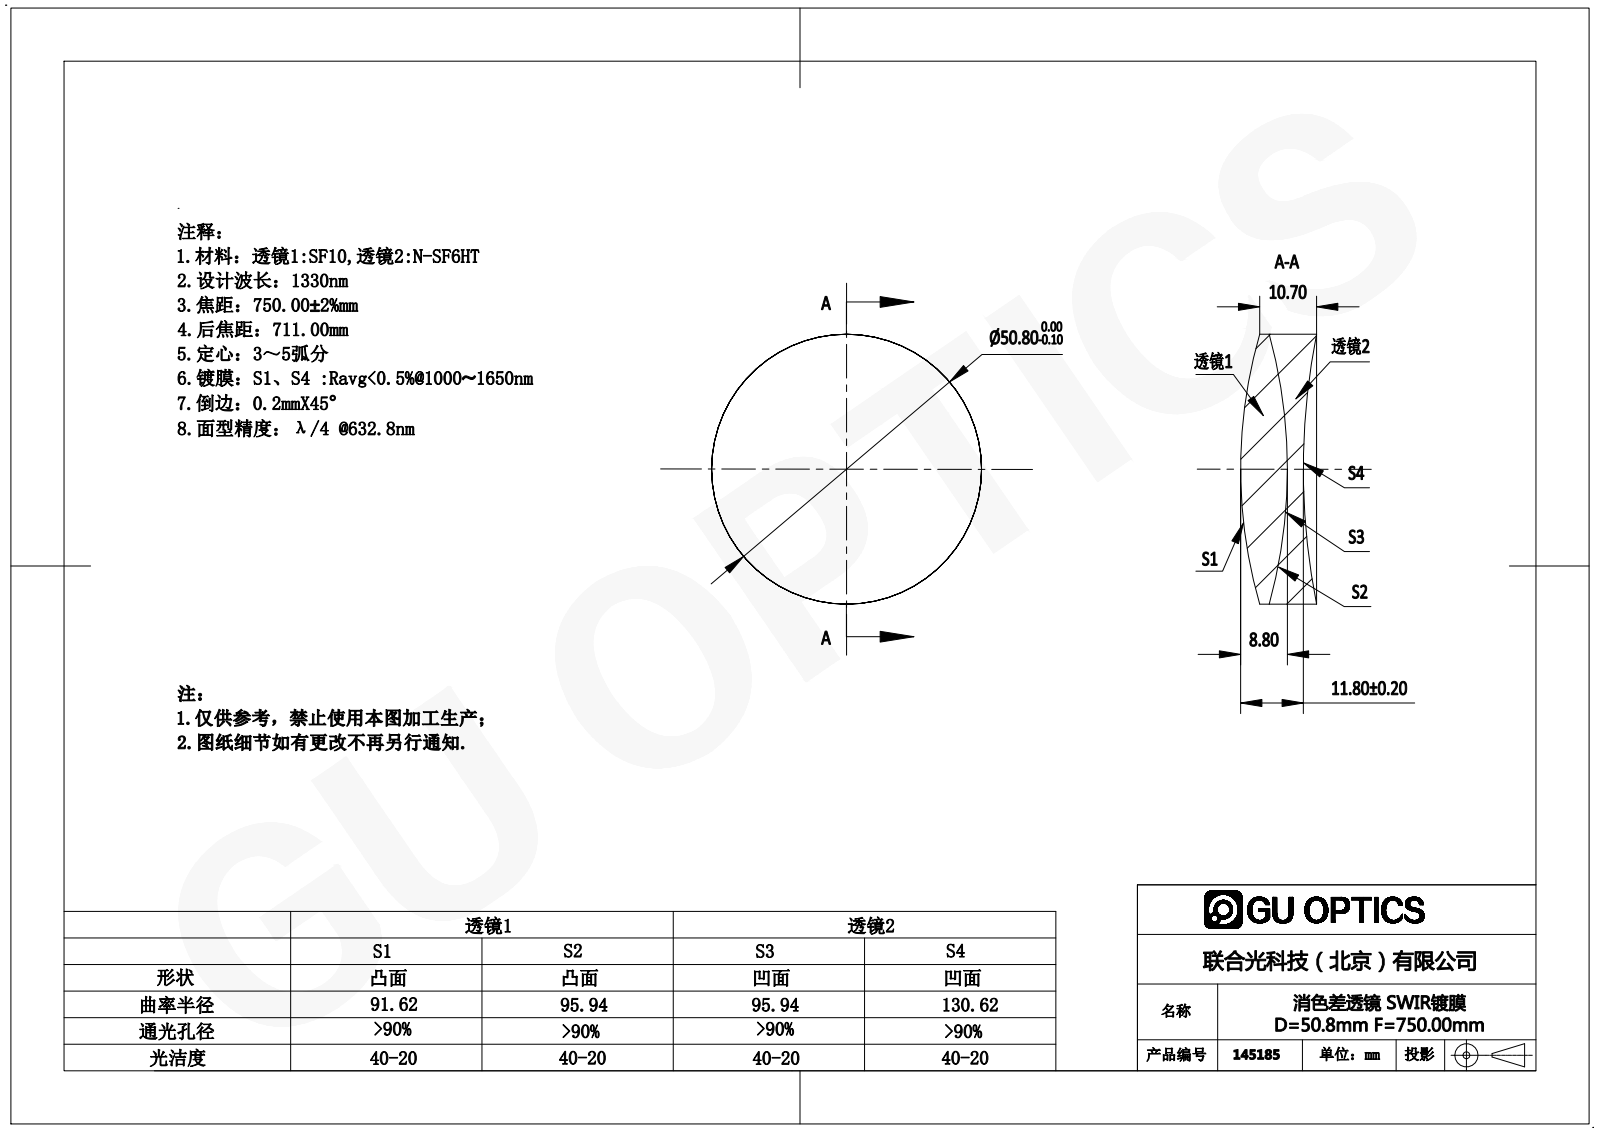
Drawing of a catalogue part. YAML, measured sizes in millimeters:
part_name: "145185"
step_written_by: "SolidWorks 2016 (AUTOMOTIVE_DESIGN)"
units: millimeters
bodies: {solids: 2, faces: 12, planar: 0, cylindrical: 4, other: 8}
overall_size: [50.8, 50.8, 14.29]
volume: 22820
surface_area: 9949
round_bosses_or_shafts:
  - {diameter: 50.8, count: 1}
